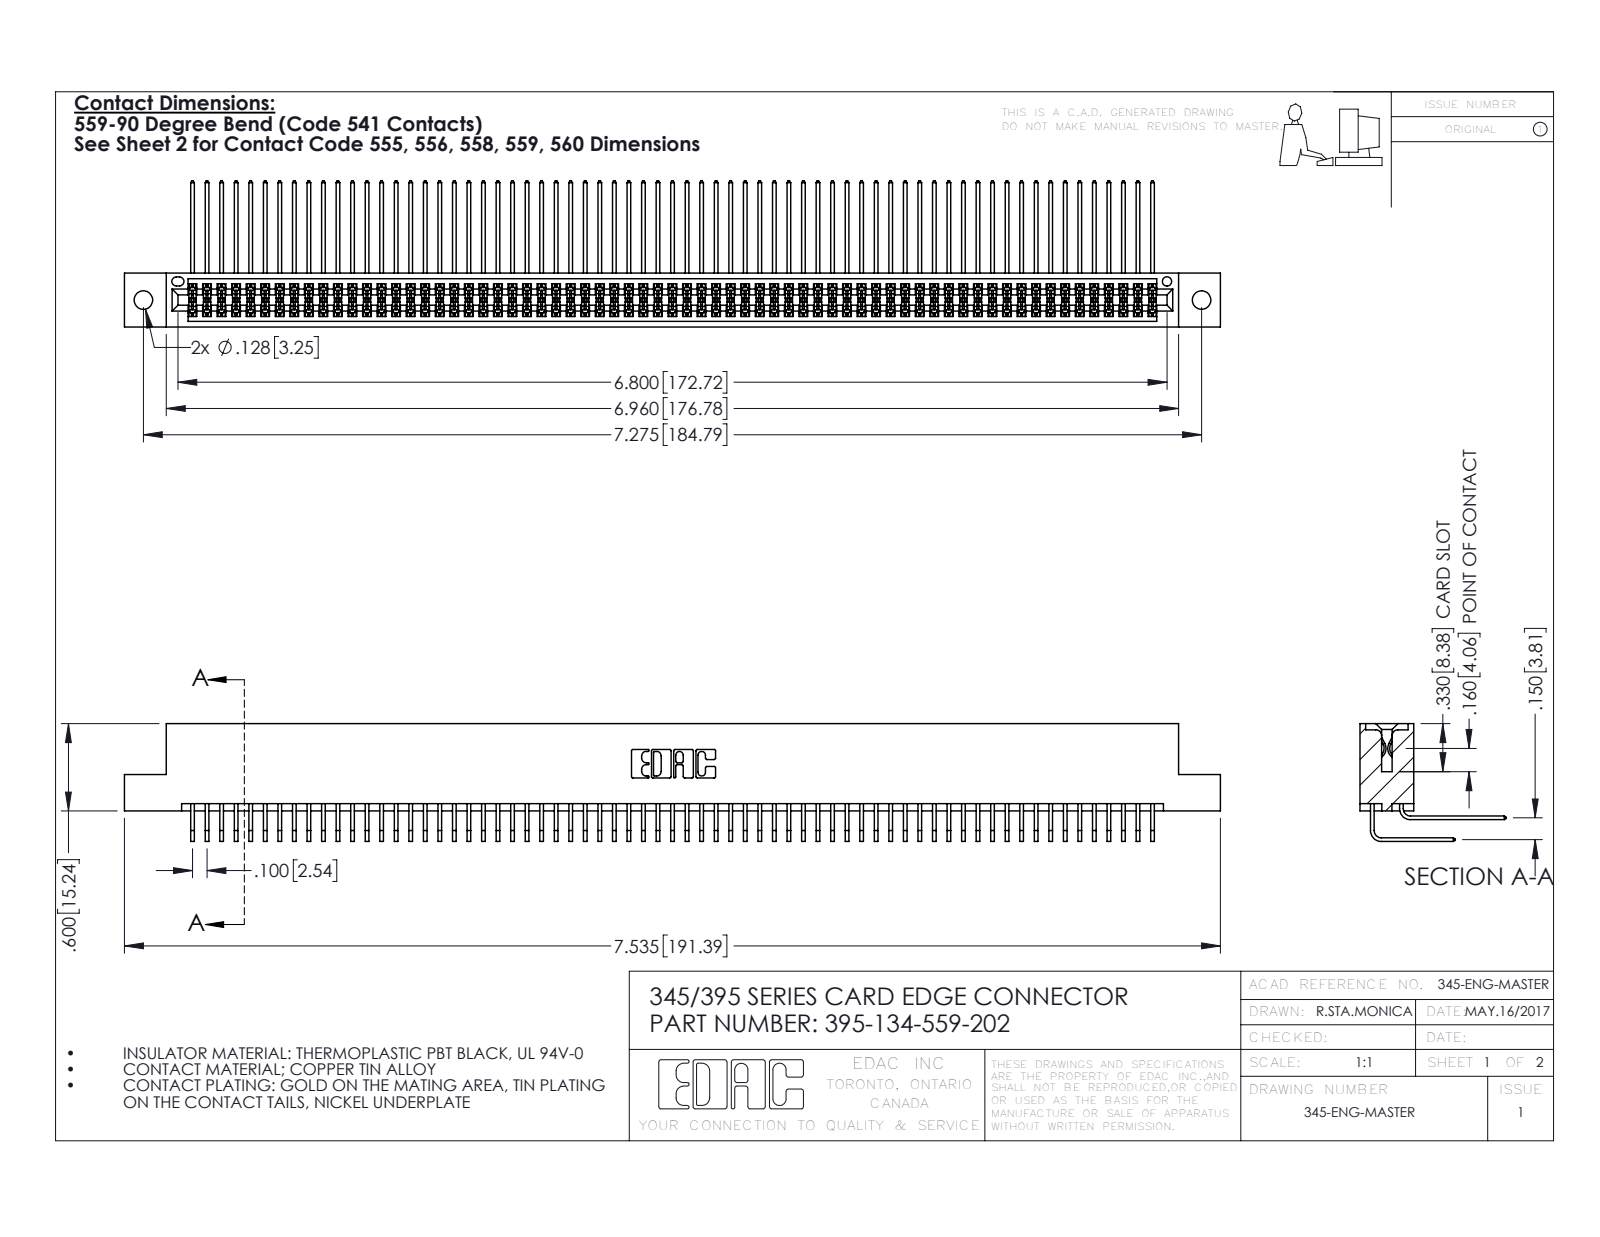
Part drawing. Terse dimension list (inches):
name: 345-292-001_558 559 Tail - 1; 345-292-001_559 Tail - 2; 345 Part_Flush Mounting Lugs - 0.128 Dia; 395-134-559-202
written by: SolidWorks 2016 (CONFIG_CONTROL_DESIGN)
unit: in
bodies: 135 solids, 7094 faces (4770 planar, 2324 cylindrical, 0 other)
size: 7.535 × 1.005 × 0.809
volume: 1.194 in³; area: 50.78 in²
holes: 2× ⌀0.128, 1× ⌀0.064
rounds: 202× R0.006, 22× R0.01, 6× R0.007, 6× R0.031, 3× R0.026, 2× R0.014, 2× R0.019, 2× R0.022
face distances: 0.072, 0.298, 0.2, 0.37, 0.098, 0.272, 0.025, 0.225, 0.175, 0.15
hole spacings: 0.27, 7.039, 7.275
